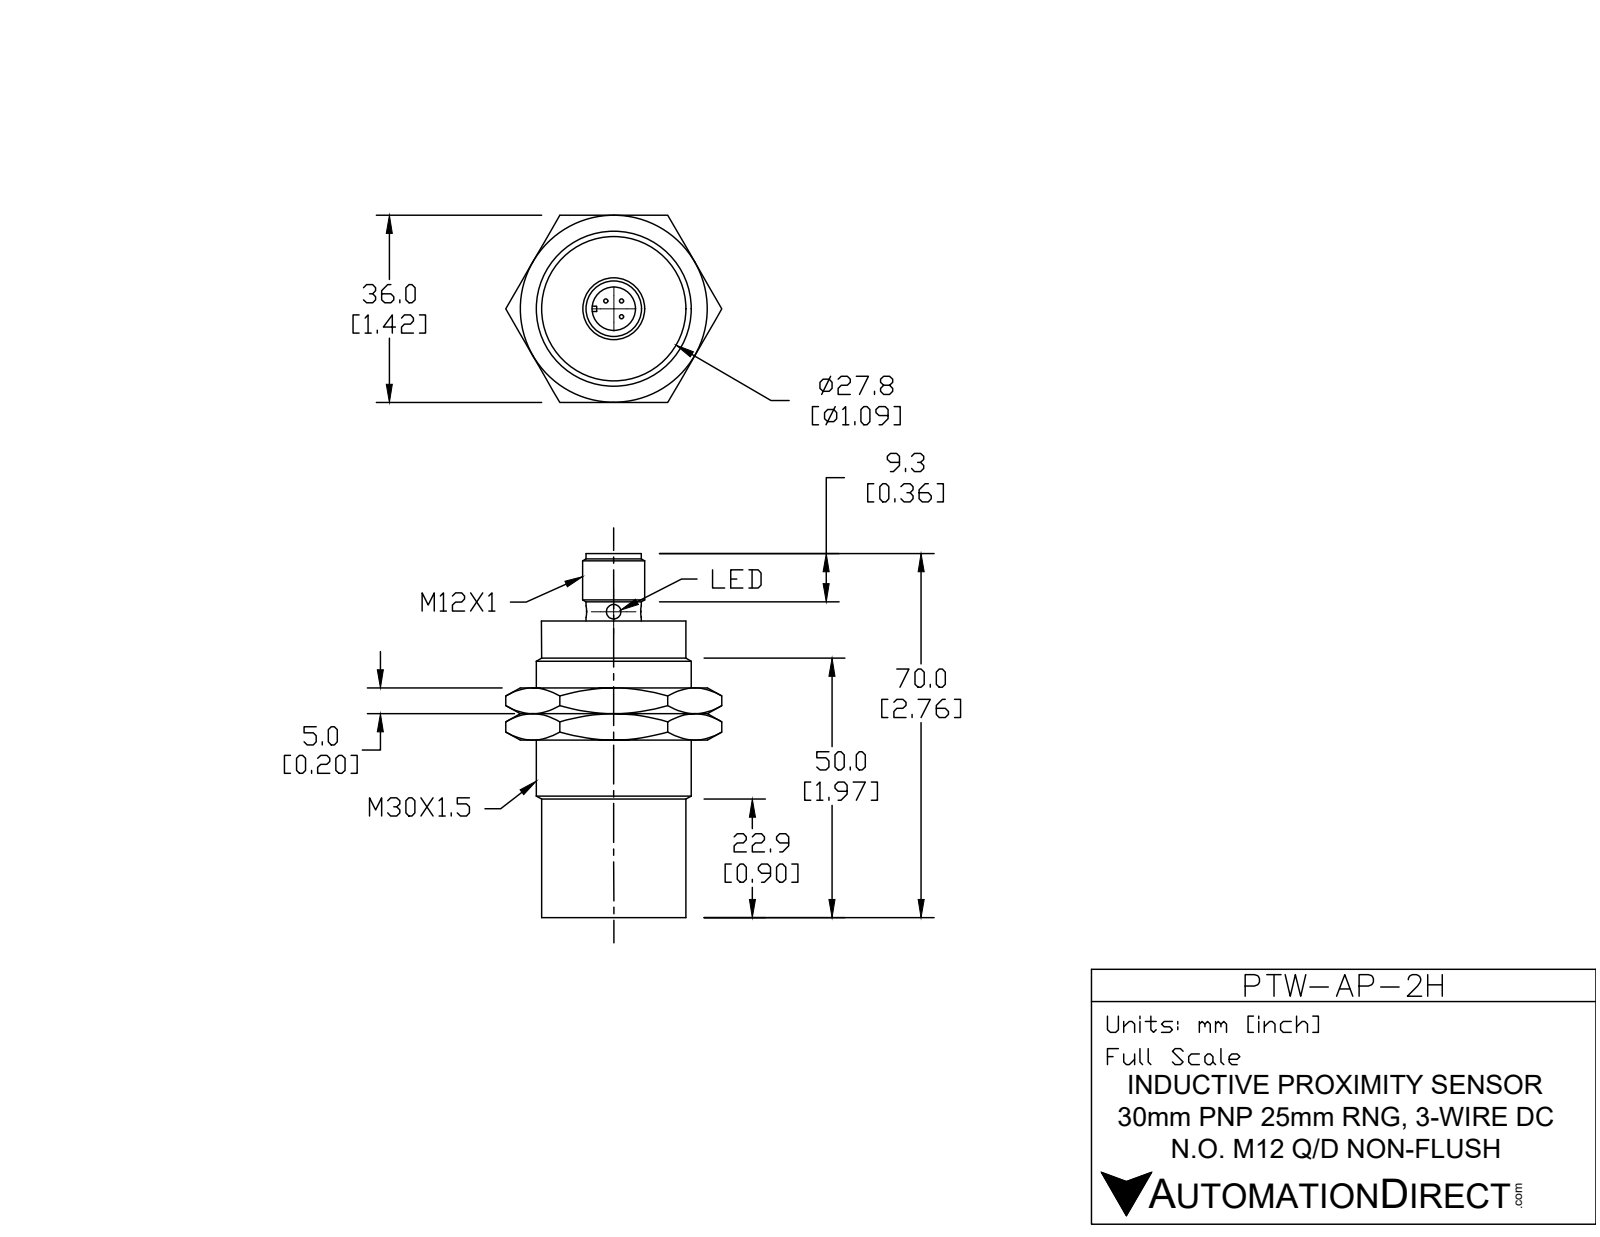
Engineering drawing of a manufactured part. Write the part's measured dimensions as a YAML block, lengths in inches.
part_name: "PTW-AP-2H"
step_written_by: "SolidWorks 2017 (AUTOMOTIVE_DESIGN)"
units: inches
bodies: {solids: 3, faces: 114, planar: 26, cylindrical: 29, other: 59}
overall_size: [2.764, 1.637, 1.417]
volume: 2.614
surface_area: 16.96
round_holes:
  - {diameter: 0.118, count: 2}
  - {diameter: 0.331, count: 1}
  - {diameter: 1.117, count: 1}
round_bosses_or_shafts:
  - {diameter: 1.181, count: 1}
  - {diameter: 1.094, count: 1}
  - {diameter: 1.093, count: 1}
  - {diameter: 0.472, count: 1}
  - {diameter: 0.445, count: 1}
  - {diameter: 0.417, count: 1}
partial_cylinders:
  - {radius: 0.024, count: 1}
face_to_face_distances: [0.197, 1.386, 1.417, 0.866, 2.252, 1.063, 1.189, 0.669, 0.394, 1.583]
